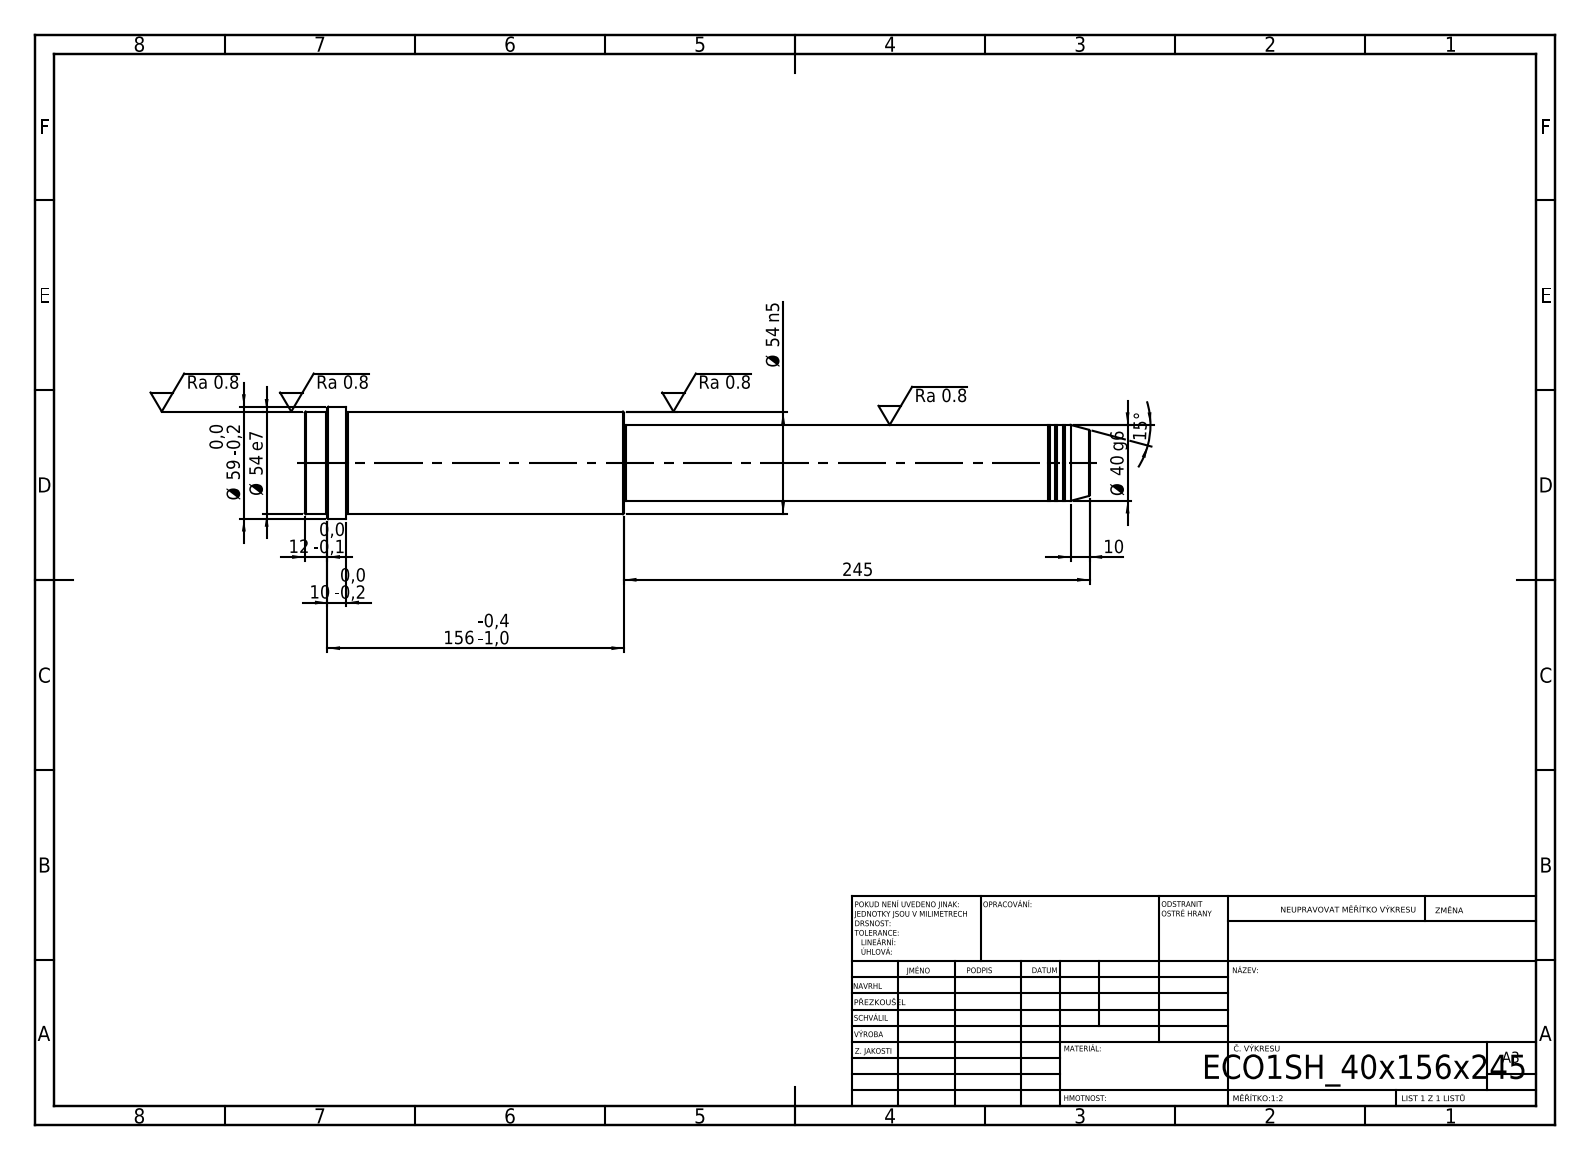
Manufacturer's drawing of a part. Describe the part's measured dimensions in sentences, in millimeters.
Its 3-D file was written by "SolidWorks 2019 (CONFIG_CONTROL_DESIGN)". It is 1 solid with 52 faces: 6 planar, 16 cylindrical and 30 other. Overall it measures 413 by 59 by 59 millimeters. Its volume is 695 053 cubic millimeters and its surface area 64 903 square millimeters. Round bosses or shafts: 1 of diameter 59, 1 of diameter 54, 1 of diameter 40, 1 of diameter 39. The main face-to-face distances are 168, 245, 413, 391, 146, 22, 401, 156, 10, 12.
